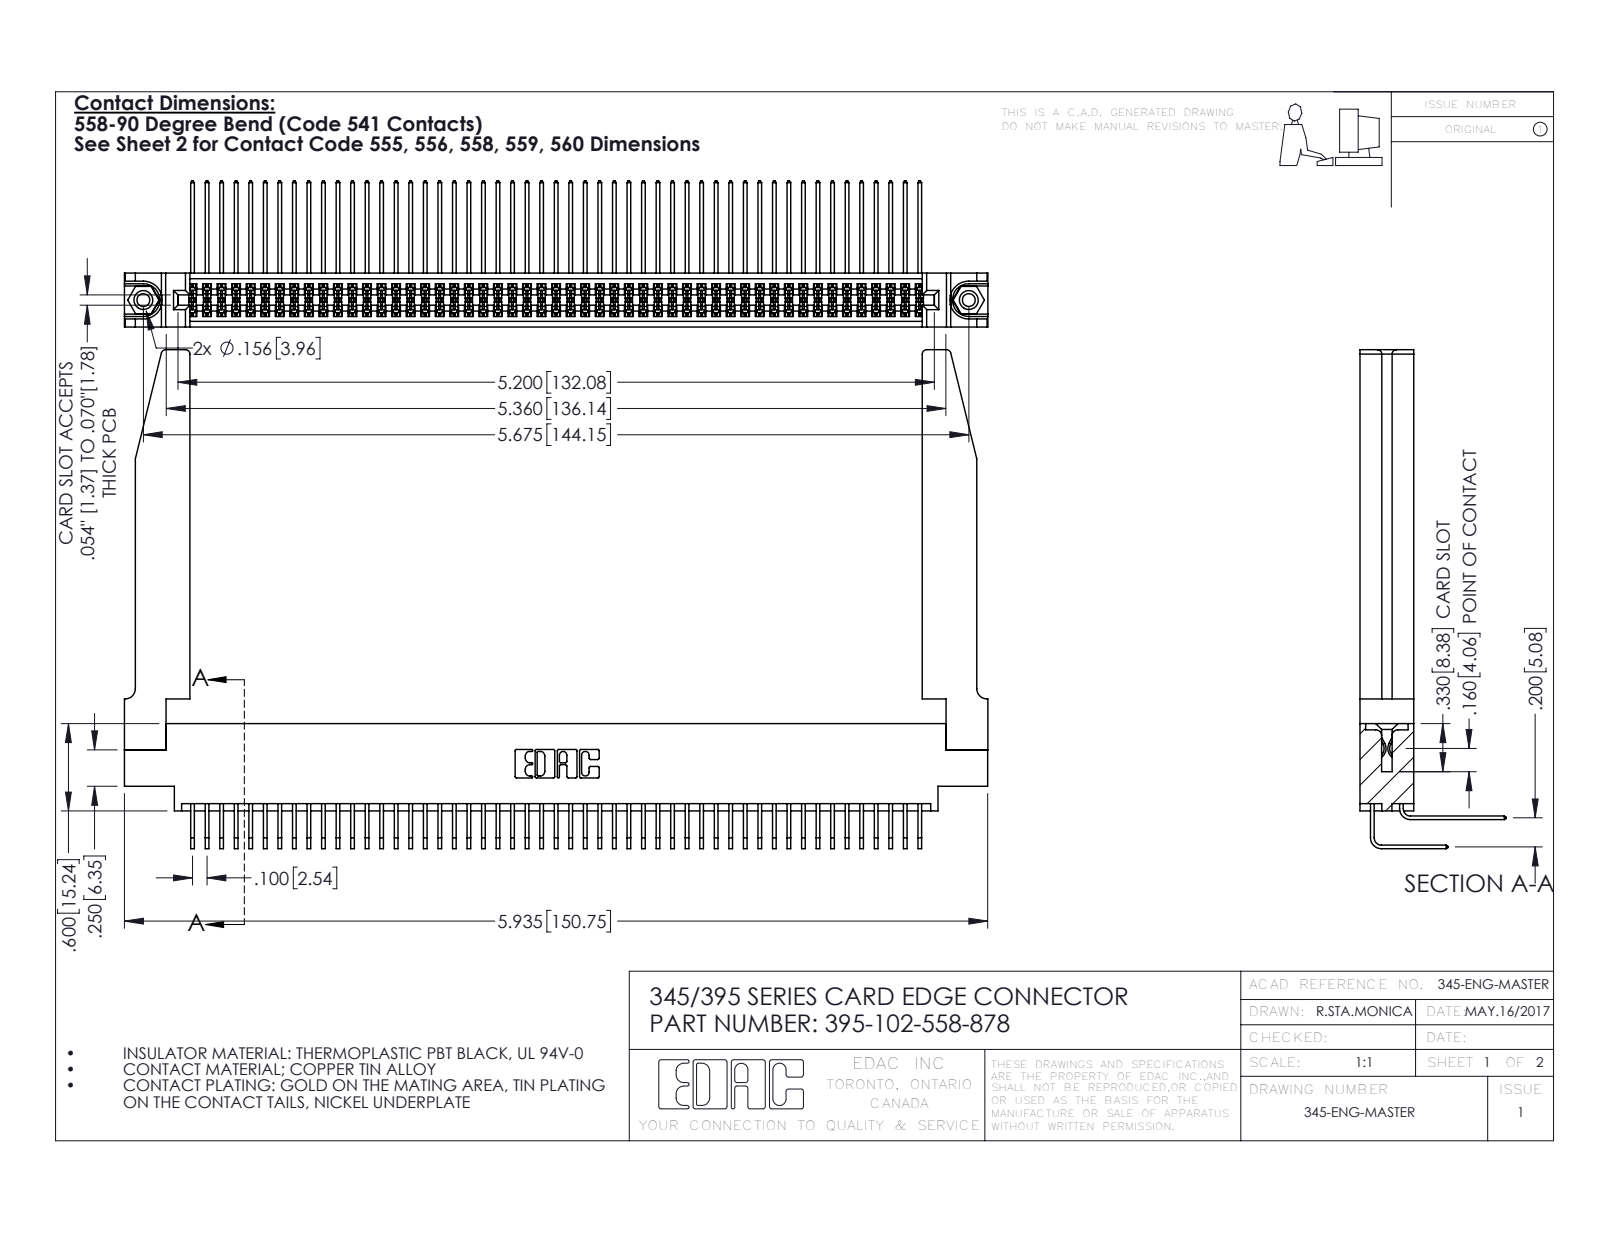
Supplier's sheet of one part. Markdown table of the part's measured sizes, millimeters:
| quantity | value |
| --- | --- |
| part name | 395-102-558-878; 345-250-001_345-250-001-102; 345-220-078_345-220-078; 345 Part_0.170 Offset - 0.156 Dia-TH (+2 more) |
| STEP written by | SolidWorks 2016 (CONFIG_CONTROL_DESIGN) |
| units | millimeters |
| bodies | 107 solids, 5668 faces (3796 planar, 1820 cylindrical, 52 other) |
| overall size | 150.8 × 87.1 × 25.5 |
| volume | 22 970 mm³ |
| surface area | 32 400 mm² |
| round holes (diameter × count) | 2.3 × 2, 3.2 × 2, 4 × 2, 1.6 × 1 |
| round bosses / shafts (diameter × count) | 3.9 × 2 |
| partial cylindrical surfaces (radius × count) | 0.2 × 154, 0.3 × 22, 0.8 × 8, 0.2 × 6, 0.8 × 6, 0.7 × 3, 0.4 × 2, 0.5 × 2 |
| main face-to-face distances | 1.8, 9.4, 7.6, 5.1, 2.5, 6.9, 0.6, 5.7, 4.4, 0.6 |
| hole center spacings | 6.9, 138.2, 144.1 |
